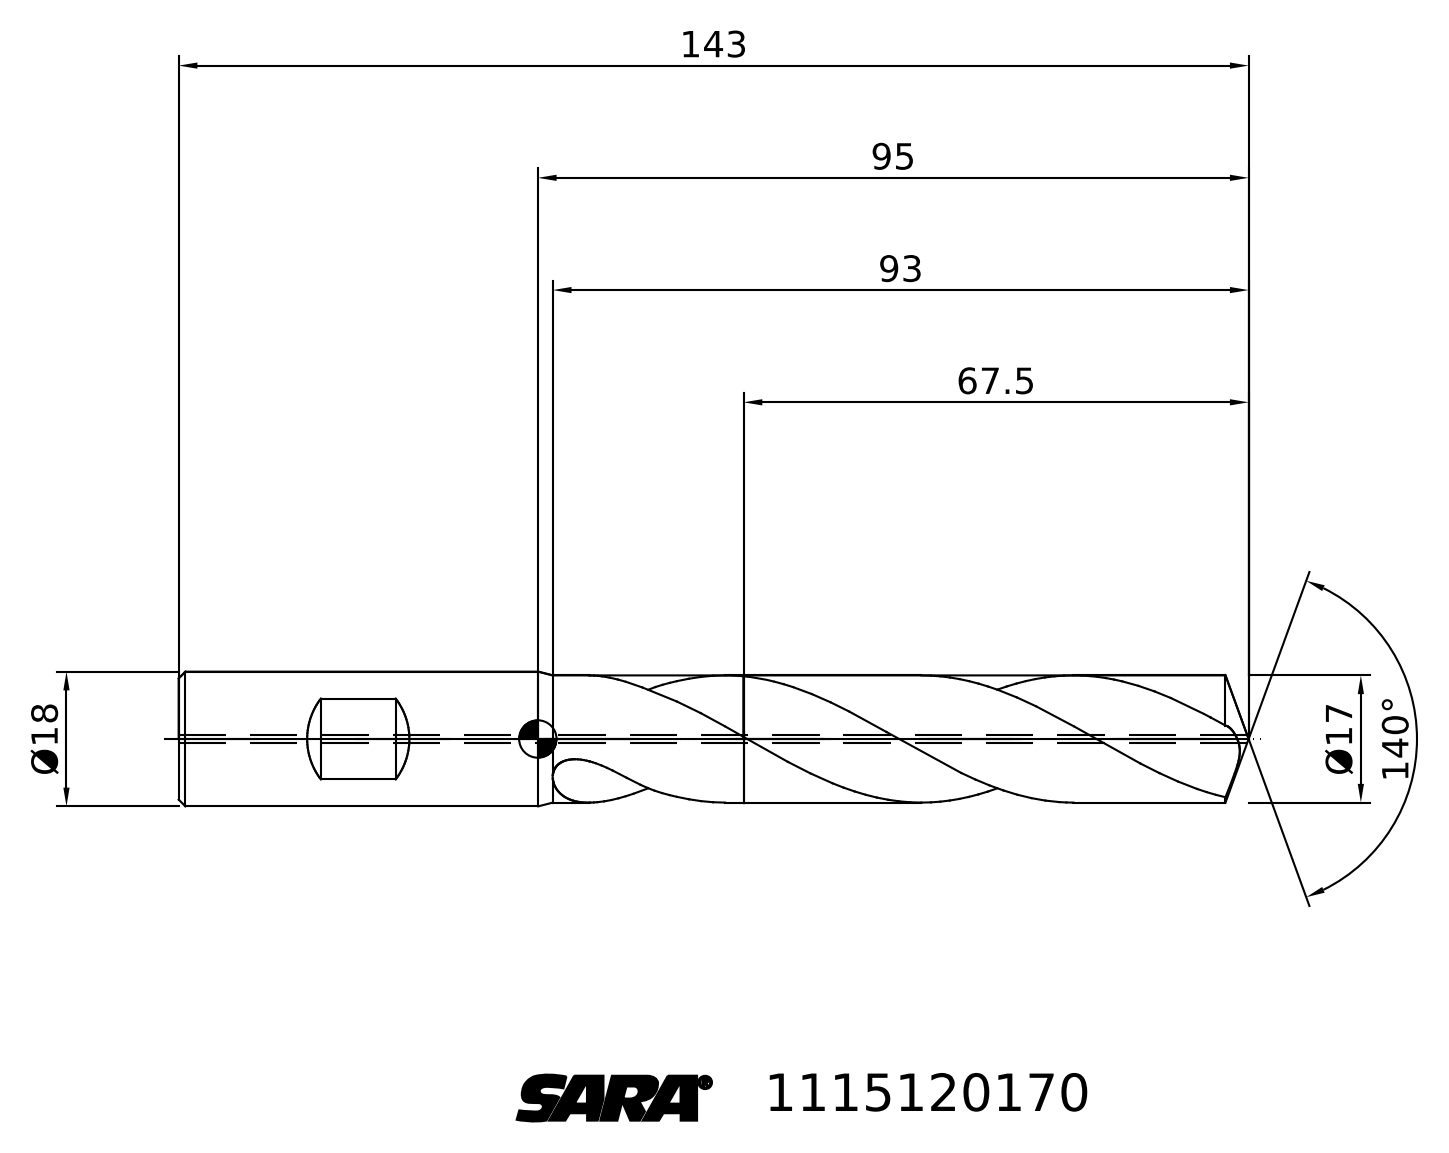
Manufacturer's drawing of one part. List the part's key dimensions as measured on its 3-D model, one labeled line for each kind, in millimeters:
STEP written by: TDM (AUTOMOTIVE_DESIGN)
Units: millimetres
Bodies: 2 solids, 30 faces (6 planar, 0 cylindrical, 24 other)
Overall size (bounding box): 143 × 45.07 × 25.48
Volume: 26 509 mm³ · Surface area: 8 770 mm²
Main face-to-face distances: 75.5
